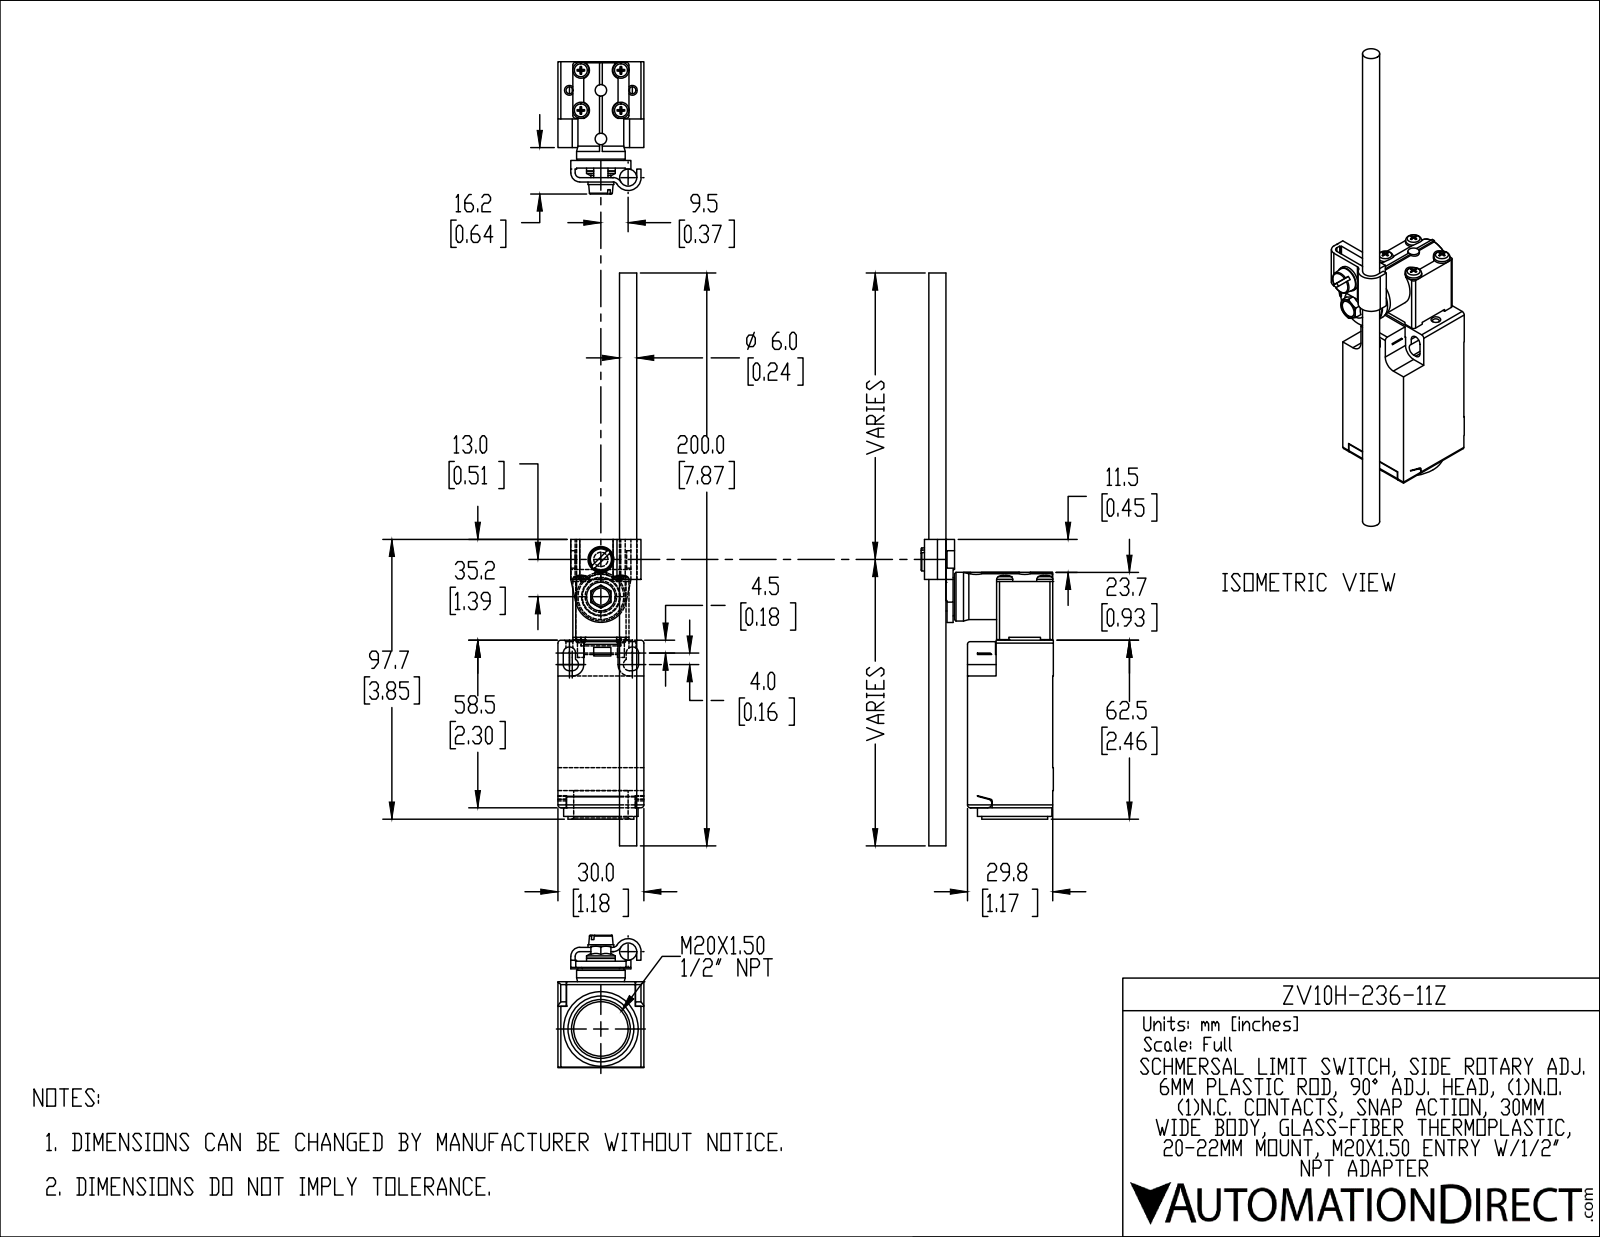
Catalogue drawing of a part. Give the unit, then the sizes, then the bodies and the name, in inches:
Units: inches
Overall size (bounding box): 7.874 × 1.819 × 1.181
Round holes (diameter × count): ⌀0.094 ×6, ⌀0.126 ×4, ⌀0.236 ×2, ⌀0.512 ×1, ⌀0.545 ×1, ⌀0.748 ×1
Round bosses / shafts (diameter × count): ⌀0.221 ×4, ⌀0.213 ×4, ⌀0.157 ×2, ⌀1.024 ×1, ⌀0.906 ×1, ⌀0.669 ×1, ⌀0.63 ×1, ⌀0.543 ×1
Partial cylindrical surfaces — rounded edges, fillets, slot ends (radius × count): R0.039 ×10, R0.085 ×6, R0.059 ×5, R0.118 ×4, R0.063 ×2, R0.122 ×2, R0.157 ×2, R0.008 ×1
Main face-to-face distances: 1.181, 1.173, 0.205, 0.976, 0.177, 0.281, 0.772, 0.236, 0.118, 1.455
Hole centre spacings: 0.317, 0.39, 0.551, 0.76, 0.308, 0.433, 0.454, 0.497
Volume: 4.096 in³ · Surface area: 32.5 in²
Bodies: 2 solids, 383 faces (268 planar, 81 cylindrical, 34 other)
Part name (STEP PRODUCT): ZV10H-236-11Z
STEP written by: SolidWorks 2019 (AUTOMOTIVE_DESIGN)
